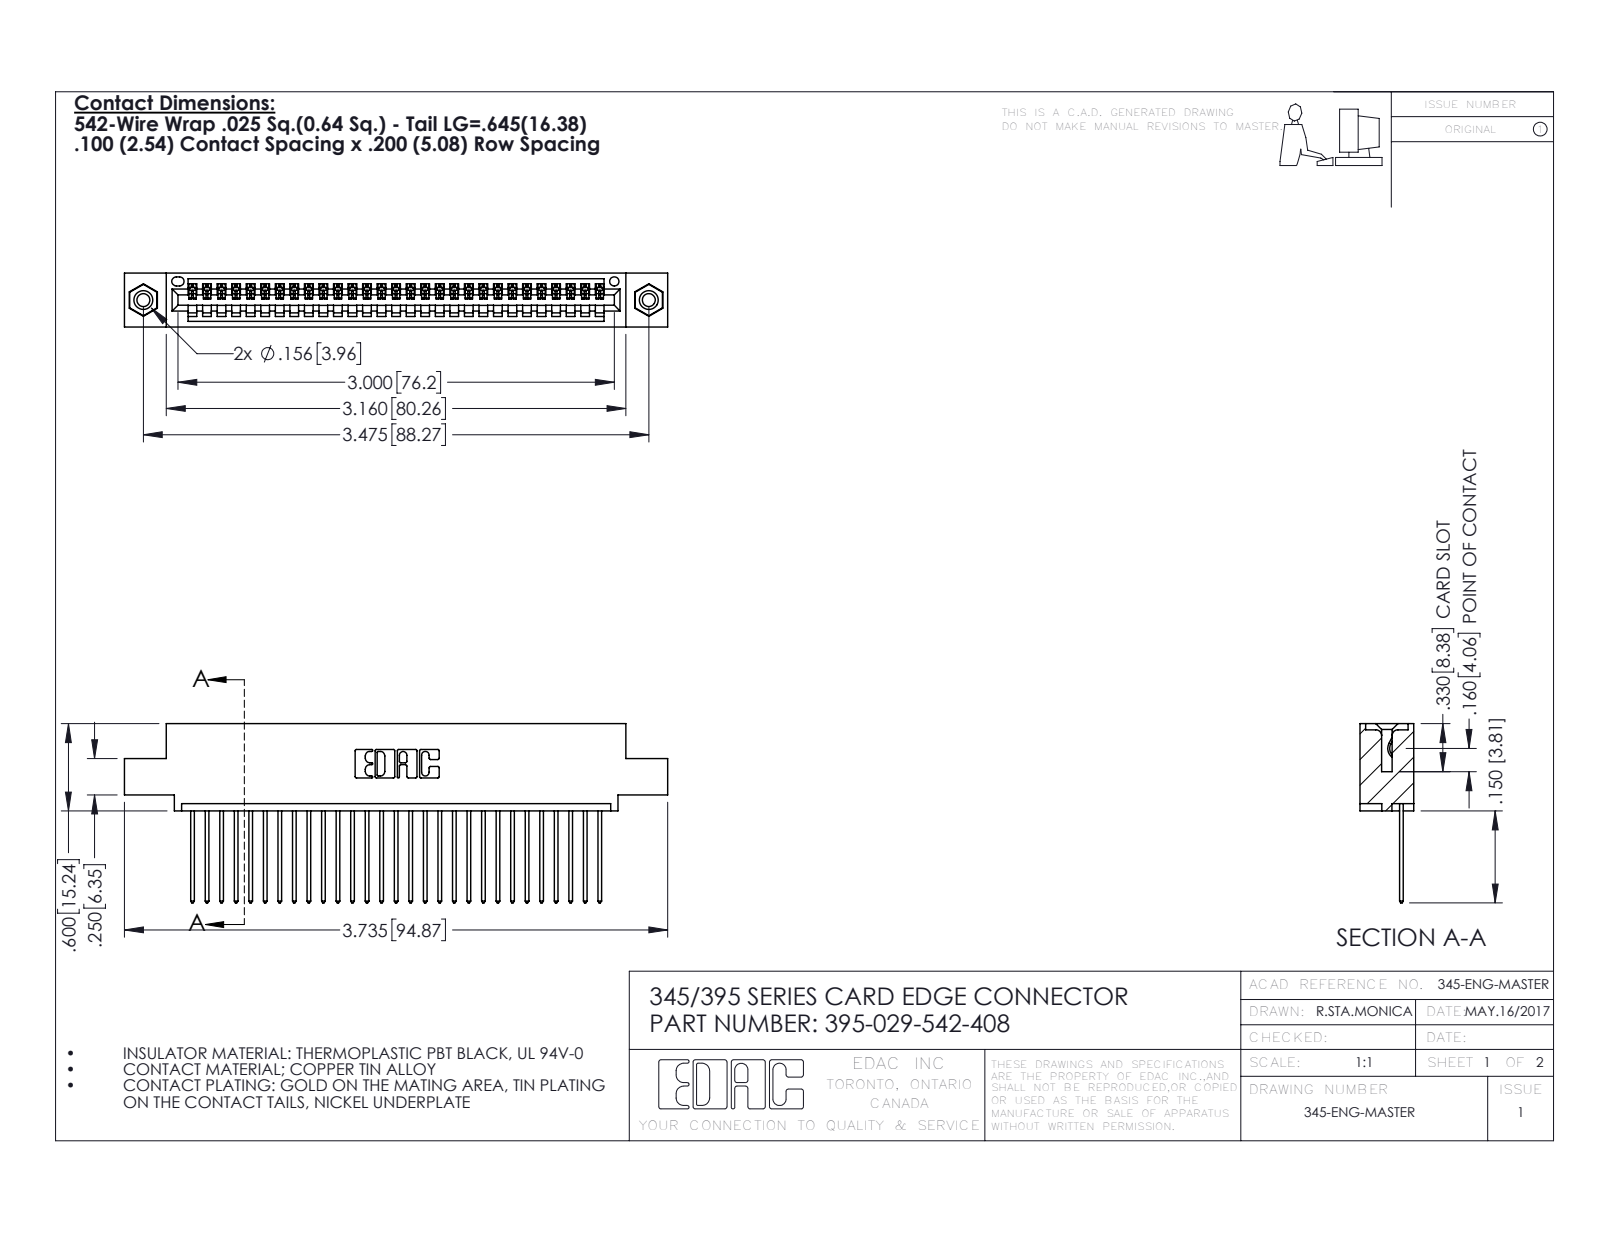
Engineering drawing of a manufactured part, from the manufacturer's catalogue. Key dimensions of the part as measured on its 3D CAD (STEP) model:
Part name (STEP PRODUCT): 395-029-542-408; 345-250-001_345-250-003-102; 345-292-001_345-293-142; 345 Part_0.110 Offset - 0.156 Dia-TI
STEP written by: SolidWorks 2016 (CONFIG_CONTROL_DESIGN)
Units: inches
Bodies: 32 solids, 1872 faces (1276 planar, 580 cylindrical, 16 other)
Overall size (bounding box): 3.735 × 1.232 × 0.37
Volume: 0.542 in³ · Surface area: 18.82 in²
Round holes (diameter × count): ⌀0.089 ×2, ⌀0.125 ×2, ⌀0.156 ×2, ⌀0.064 ×1
Round bosses / shafts (diameter × count): ⌀0.155 ×2
Partial cylindrical surfaces — rounded edges, fillets, slot ends (radius × count): R0.006 ×58, R0.01 ×58, R0.01 ×22, R0.007 ×6, R0.031 ×6, R0.026 ×3, R0.031 ×2, R0.04 ×2
Main face-to-face distances: 0.072, 0.298, 0.37, 0.098, 0.272, 0.025, 0.2, 0.225, 0.149, 0.072
Hole centre spacings: 0.27, 3.24, 3.475
